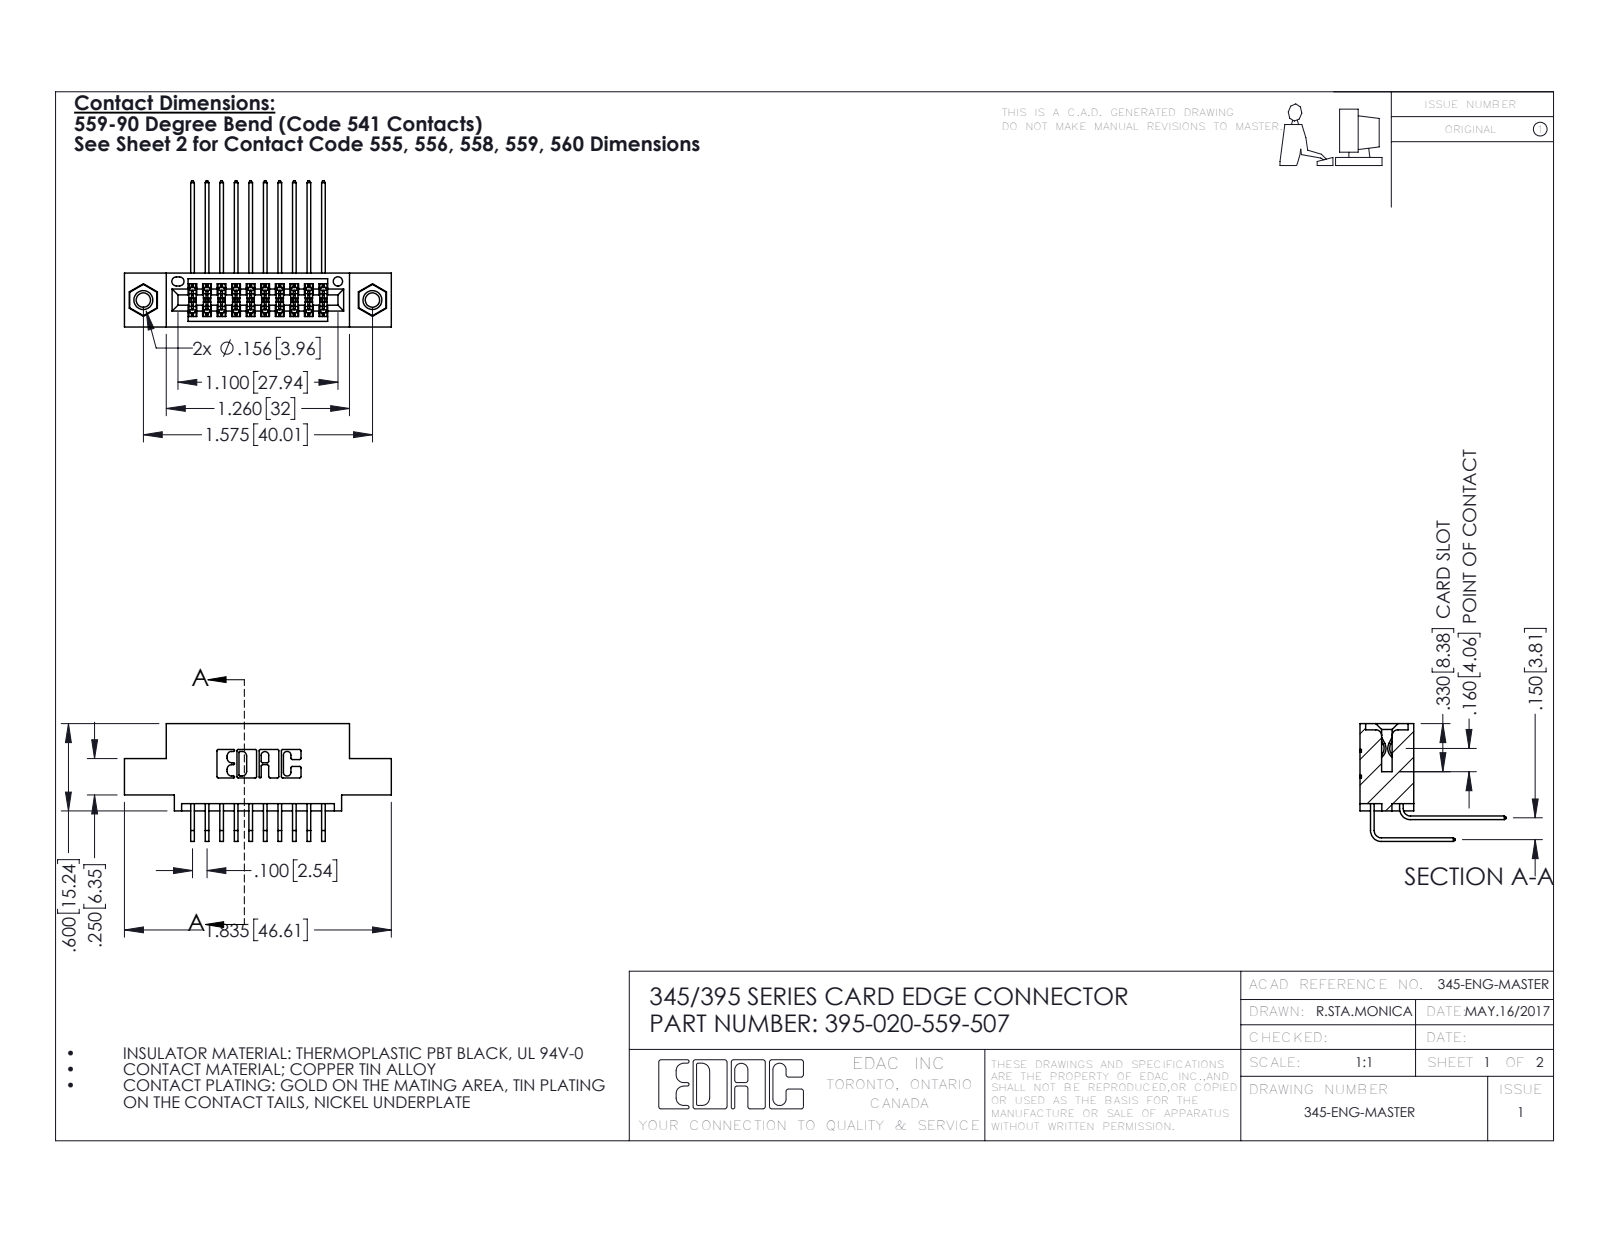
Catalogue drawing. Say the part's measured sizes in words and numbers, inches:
The part is named "345-292-001_559 Tail - 2; 345-292-001_558 559 Tail - 1; 345-250-001_345-250-005-103; 345 Part_0.110 Offset - 0.156 Dia-TI (+1 more)". Its 3-D file was written by "SolidWorks 2016 (CONFIG_CONTROL_DESIGN)". It is 23 solids with 1230 faces: 816 planar, 398 cylindrical and 16 other. Overall it measures 1.835 by 1.005 by 0.809 inches. Its volume is 0.26 cubic inches and its surface area 9.826 square inches. Round holes: 2 of diameter 0.098, 2 of diameter 0.125, 2 of diameter 0.156, 1 of diameter 0.064. Round bosses or shafts: 2 of diameter 0.155. Partial cylindrical surfaces (rounded edges, fillets, slot ends): 31 of radius 0.006, 22 of radius 0.01, 6 of radius 0.007, 6 of radius 0.031, 3 of radius 0.026, 2 of radius 0.014, 2 of radius 0.019, 2 of radius 0.022. The main face-to-face distances are 0.2, 0.072, 0.298, 0.37, 0.1, 0.098, 0.272, 0.025, 0.6, 0.15. The hole center spacings are 0.27, 1.344, 1.575.
